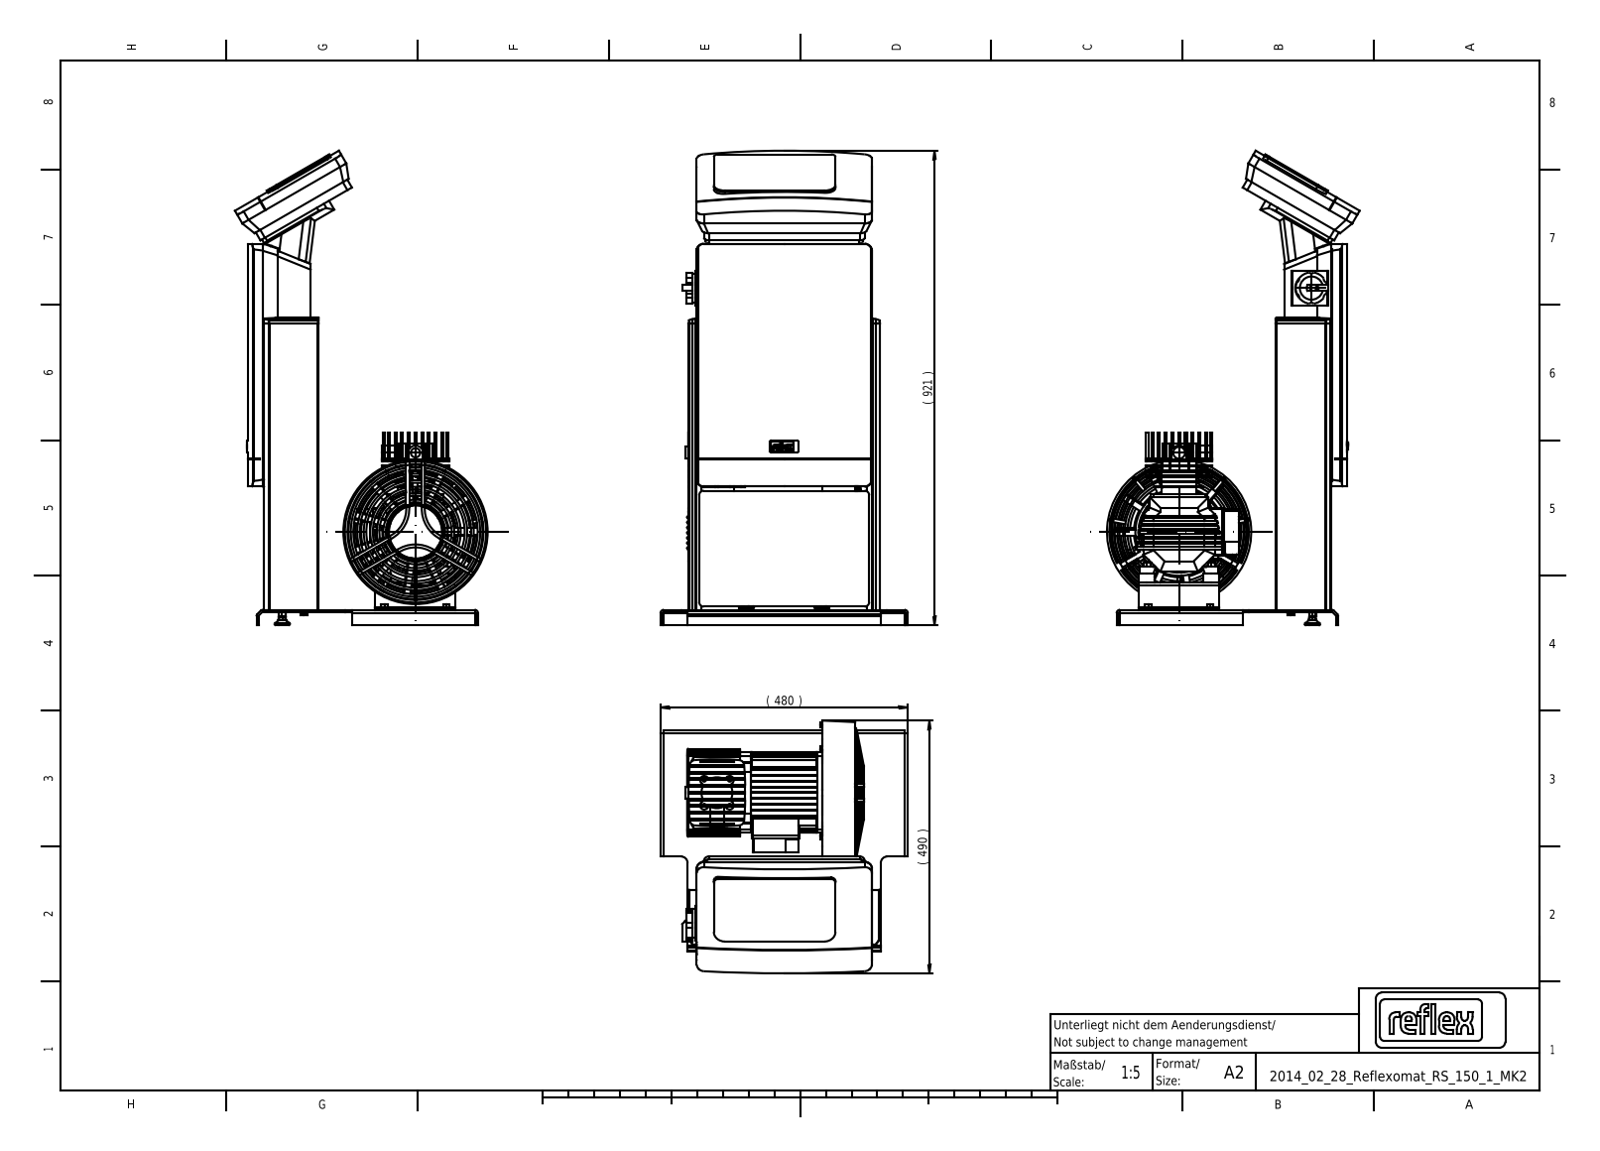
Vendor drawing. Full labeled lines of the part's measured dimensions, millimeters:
STEP written by: Mechanical Desktop 2011 (CONFIG_CONTROL_DESIGN)
Units: millimetres
Bodies: 107 solids, 3924 faces (1931 planar, 1056 cylindrical, 937 other)
Overall size (bounding box): 920.68 × 490.37 × 480
Volume: 33 220 000 mm³ · Surface area: 3 443 000 mm²
Round holes (diameter × count): ⌀17.5 ×13, ⌀9 ×12, ⌀7 ×11, ⌀10.5 ×9, ⌀6.5 ×8, ⌀17 ×8, ⌀5.5 ×6, ⌀13.5 ×4, ⌀5.4 ×3, ⌀20.5 ×3, ⌀18 ×2, ⌀23 ×2
Round bosses / shafts (diameter × count): ⌀16 ×16, ⌀20 ×12, ⌀8 ×12, ⌀19 ×9, ⌀11.2 ×9, ⌀5.1 ×9, ⌀17.5 ×8, ⌀23 ×6
Partial cylindrical surfaces — rounded edges, fillets, slot ends (radius × count): R2.5 ×30, R3 ×29, R1 ×25, R10 ×20, R2 ×12, R3.35 ×12, R5 ×12, R4.5 ×6
Main face-to-face distances: 4, 15, 10, 92, 77, 3, 2.5, 20, 346.02, 2
Hole centre spacings: 31, 45, 62, 125.02, 36, 68.02, 81.87, 93
